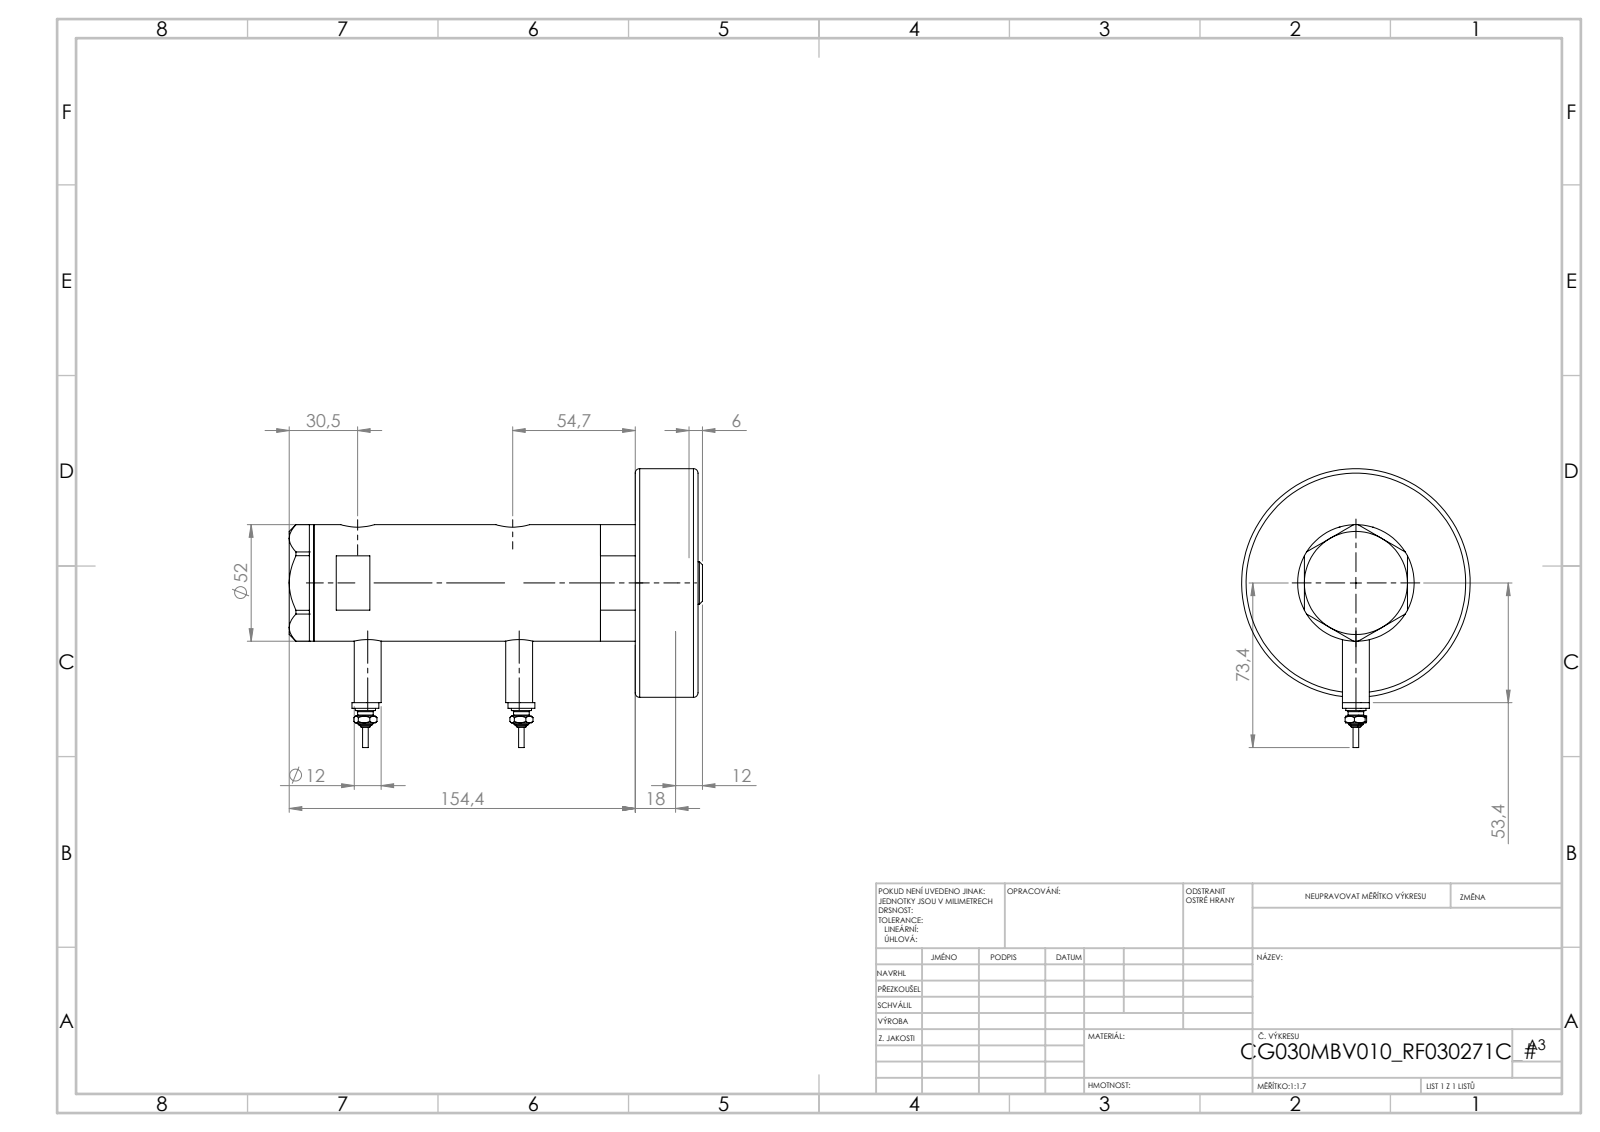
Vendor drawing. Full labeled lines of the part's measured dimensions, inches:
Part name (STEP PRODUCT): V270CG_VC; V270CG_MIDDLE; V270CG_BACK; V270CG_271C (+2 more)
STEP written by: SolidWorks 2019 (CONFIG_CONTROL_DESIGN)
Units: inches
Bodies: 7 solids, 236 faces (95 planar, 73 cylindrical, 68 other)
Overall size (bounding box): 7.26 × 4.898 × 4.016
Volume: 33.07 in³ · Surface area: 164.8 in²
Round holes (diameter × count): ⌀0.383 ×2, ⌀0.492 ×2, ⌀0.591 ×2, ⌀0.256 ×1, ⌀0.787 ×1, ⌀0.846 ×1, ⌀1.181 ×1, ⌀1.299 ×1, ⌀1.575 ×1, ⌀1.732 ×1
Round bosses / shafts (diameter × count): ⌀0.472 ×4, ⌀0.354 ×2, ⌀0.276 ×2, ⌀0.177 ×2, ⌀0.098 ×2, ⌀4.016 ×1, ⌀2.047 ×1, ⌀1.496 ×1
Main face-to-face distances: 1.102, 5.646, 6.748, 3.146, 3.602, 2.043, 0.937, 2.665, 4.709, 5.811
Hole centre spacings: 0.114, 0.177, 2.547, 2.661, 2.724, 2.839
